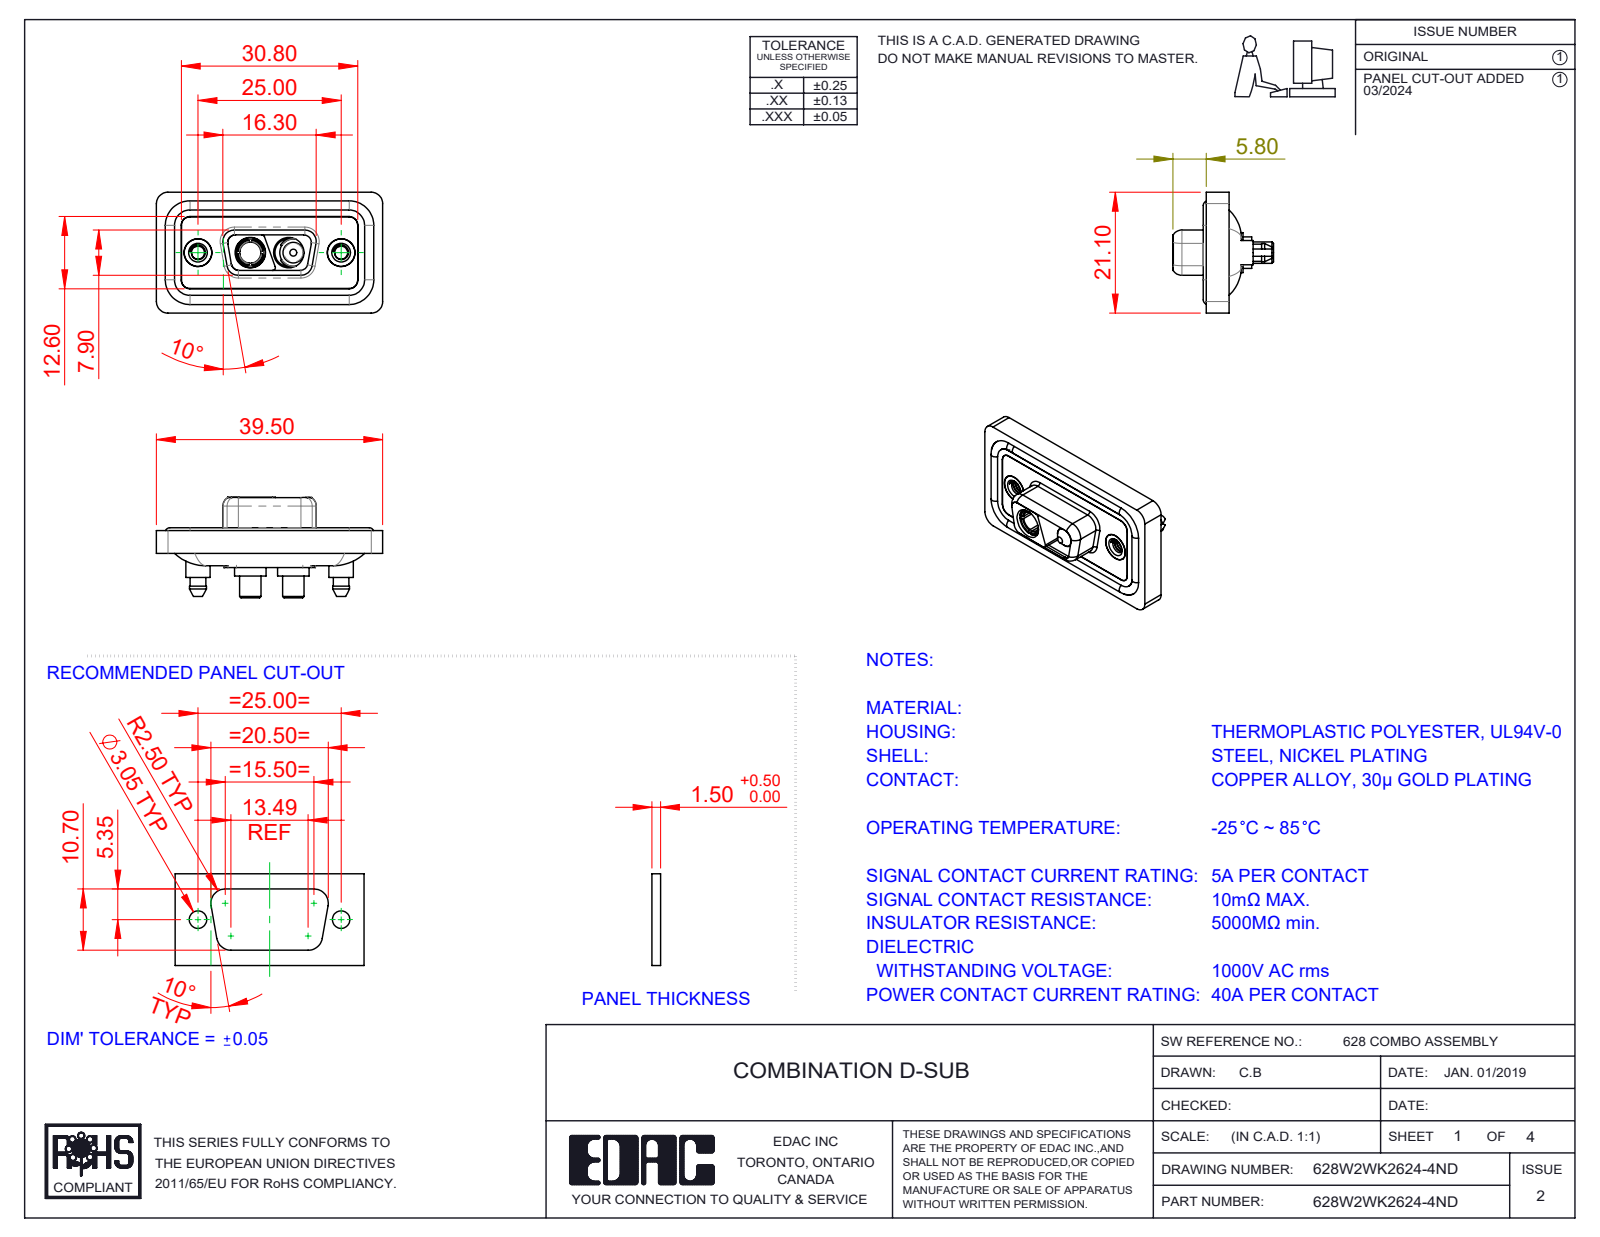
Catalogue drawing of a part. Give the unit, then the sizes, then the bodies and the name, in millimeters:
Units: millimetres
Overall size (bounding box): 39.5 × 21.1 × 17.55
Round holes (diameter × count): ⌀4.85 ×4, ⌀2.26 ×2, ⌀4 ×2, ⌀4.05 ×2, ⌀5 ×2, ⌀5.3 ×2, ⌀3.7 ×1
Round bosses / shafts (diameter × count): ⌀1.6 ×4, ⌀5.5 ×2, ⌀5.4 ×2, ⌀5.2 ×2, ⌀4.95 ×2, ⌀4.8 ×2, ⌀4.75 ×2, ⌀4.25 ×2
Partial cylindrical surfaces — rounded edges, fillets, slot ends (radius × count): R1.5 ×24, R2 ×18, R1.6 ×10, R1.35 ×8, R0.5 ×6, R0.25 ×4, R0.6 ×4, R0.65 ×4
Main face-to-face distances: 0.4, 1.1, 2.9, 1.6, 0.5, 1.8, 5.65, 4, 1.5, 5.35
Hole centre spacings: 9.14, 15.86, 6.72, 25
Volume: 4 775 mm³ · Surface area: 7 705 mm²
Bodies: 11 solids, 566 faces (160 planar, 279 cylindrical, 127 other)
Part name (STEP PRODUCT): 628Combo Shell Rear_09 Contacts; 628Combo Shell Front_09 Contacts; 628Combo Threaded Boardlock_D; Power Socket_40A S (+4 more)
STEP written by: SolidWorks 2023 (CONFIG_CONTROL_DESIGN)
